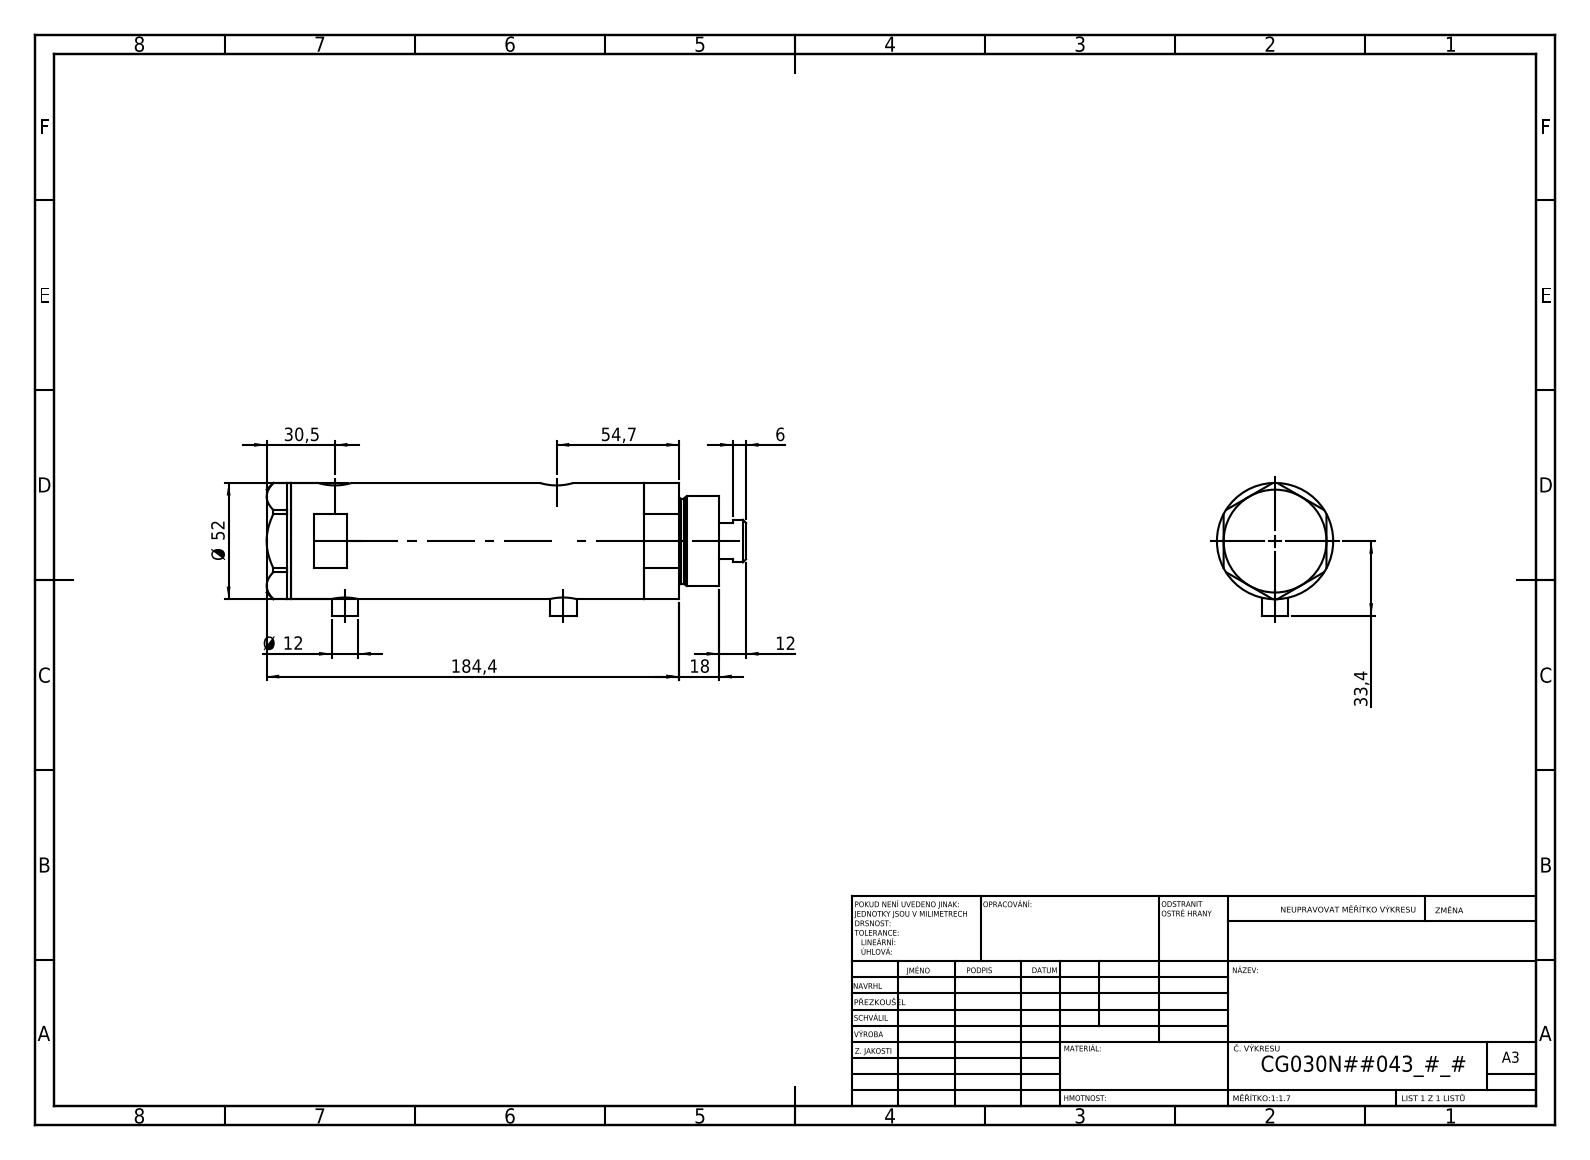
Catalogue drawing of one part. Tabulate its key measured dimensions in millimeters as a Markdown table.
| quantity | value |
| --- | --- |
| part name | V270CG_BACK; V270CG_MIDDLE; V270CG_FRONT; V270CG_VC |
| STEP written by | SolidWorks 2019 (CONFIG_CONTROL_DESIGN) |
| units | millimeters |
| bodies | 4 solids, 134 faces (65 planar, 49 cylindrical, 20 other) |
| overall size | 214.4 × 59.4 × 52 |
| volume | 393 526 mm³ |
| surface area | 87 282 mm² |
| round holes (diameter × count) | 9.73 × 2, 12.5 × 2, 15 × 2, 6.5 × 1, 20 × 1, 21.5 × 1, 30 × 1, 33 × 1, 44 × 1 |
| round bosses / shafts (diameter × count) | 12 × 2, 52 × 1, 40 × 1, 38 × 1, 19 × 1 |
| main face-to-face distances | 121.5, 23.8, 97.7, 11, 34.8, 132.5, 46, 168.9, 157.9, 134.1 |
| hole center spacings | 2.9, 4.5, 94.7, 97.6, 99.2, 102.1 |
